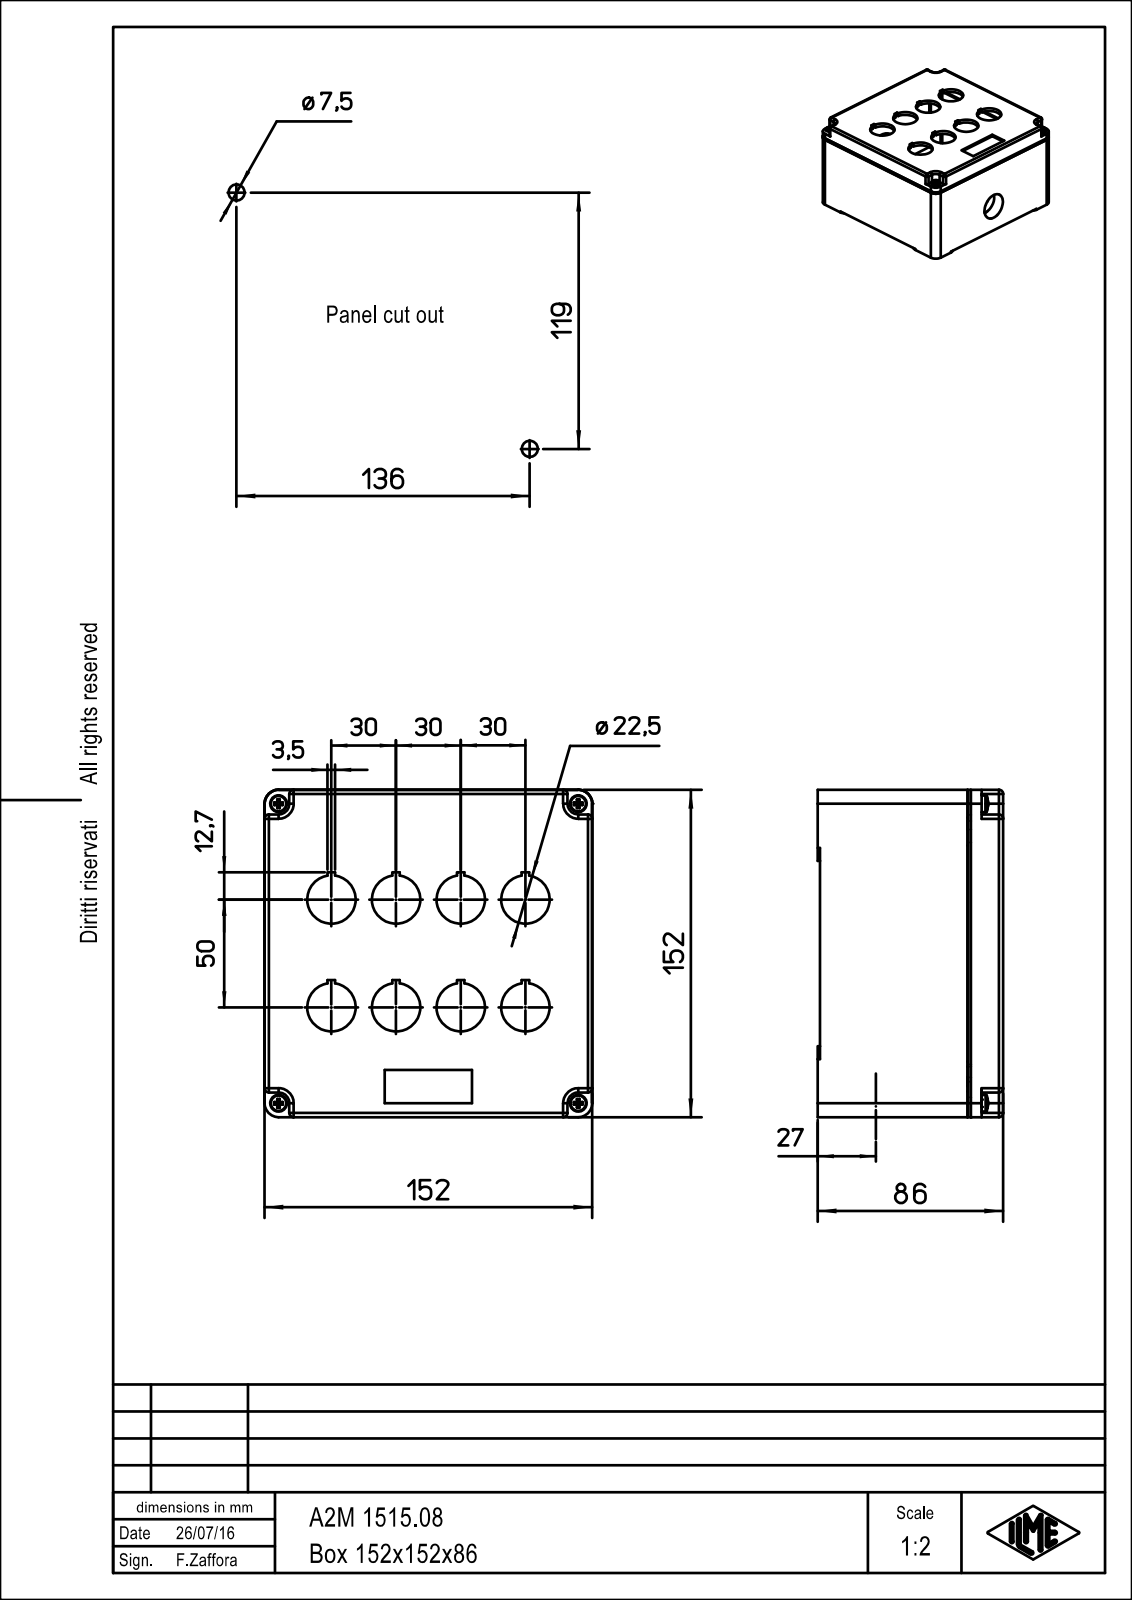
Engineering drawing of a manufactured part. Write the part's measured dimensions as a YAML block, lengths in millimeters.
part_name: "COVER; BOX; A2M_1515.08"
step_written_by: "PTC Creo Elements/Direct Modeling 19.0B 21-Mar-2015 (C) Parametric Technology GmbH (AUTOMOTIVE_DESIGN)"
units: millimeters
bodies: {solids: 2, faces: 1047, planar: 811, cylindrical: 193, other: 43}
overall_size: [152.02, 152, 86]
volume: 377105
surface_area: 201430
round_holes:
  - {diameter: 22.5, count: 8}
  - {diameter: 3.3, count: 6}
  - {diameter: 4.5, count: 4}
  - {diameter: 5.8, count: 2}
  - {diameter: 7.5, count: 2}
  - {diameter: 10.6, count: 1}
  - {diameter: 10.61, count: 1}
  - {diameter: 23.4, count: 1}
round_bosses_or_shafts:
  - {diameter: 7.8, count: 4}
  - {diameter: 4, count: 4}
  - {diameter: 6.2, count: 2}
  - {diameter: 6, count: 2}
  - {diameter: 7, count: 1}
partial_cylinders:
  - {radius: 0.33, count: 22}
  - {radius: 2, count: 17}
  - {radius: 6, count: 12}
  - {radius: 6.5, count: 12}
  - {radius: 5, count: 6}
  - {radius: 8, count: 6}
  - {radius: 0.27, count: 4}
  - {radius: 0.27, count: 4}
face_to_face_distances: [3, 82, 152, 85, 79, 4.38, 147.63, 147.62, 4.37, 143.25]
hole_center_spacings: [139, 30, 58.31, 95.5, 122.84, 196.58, 50, 50.8]
